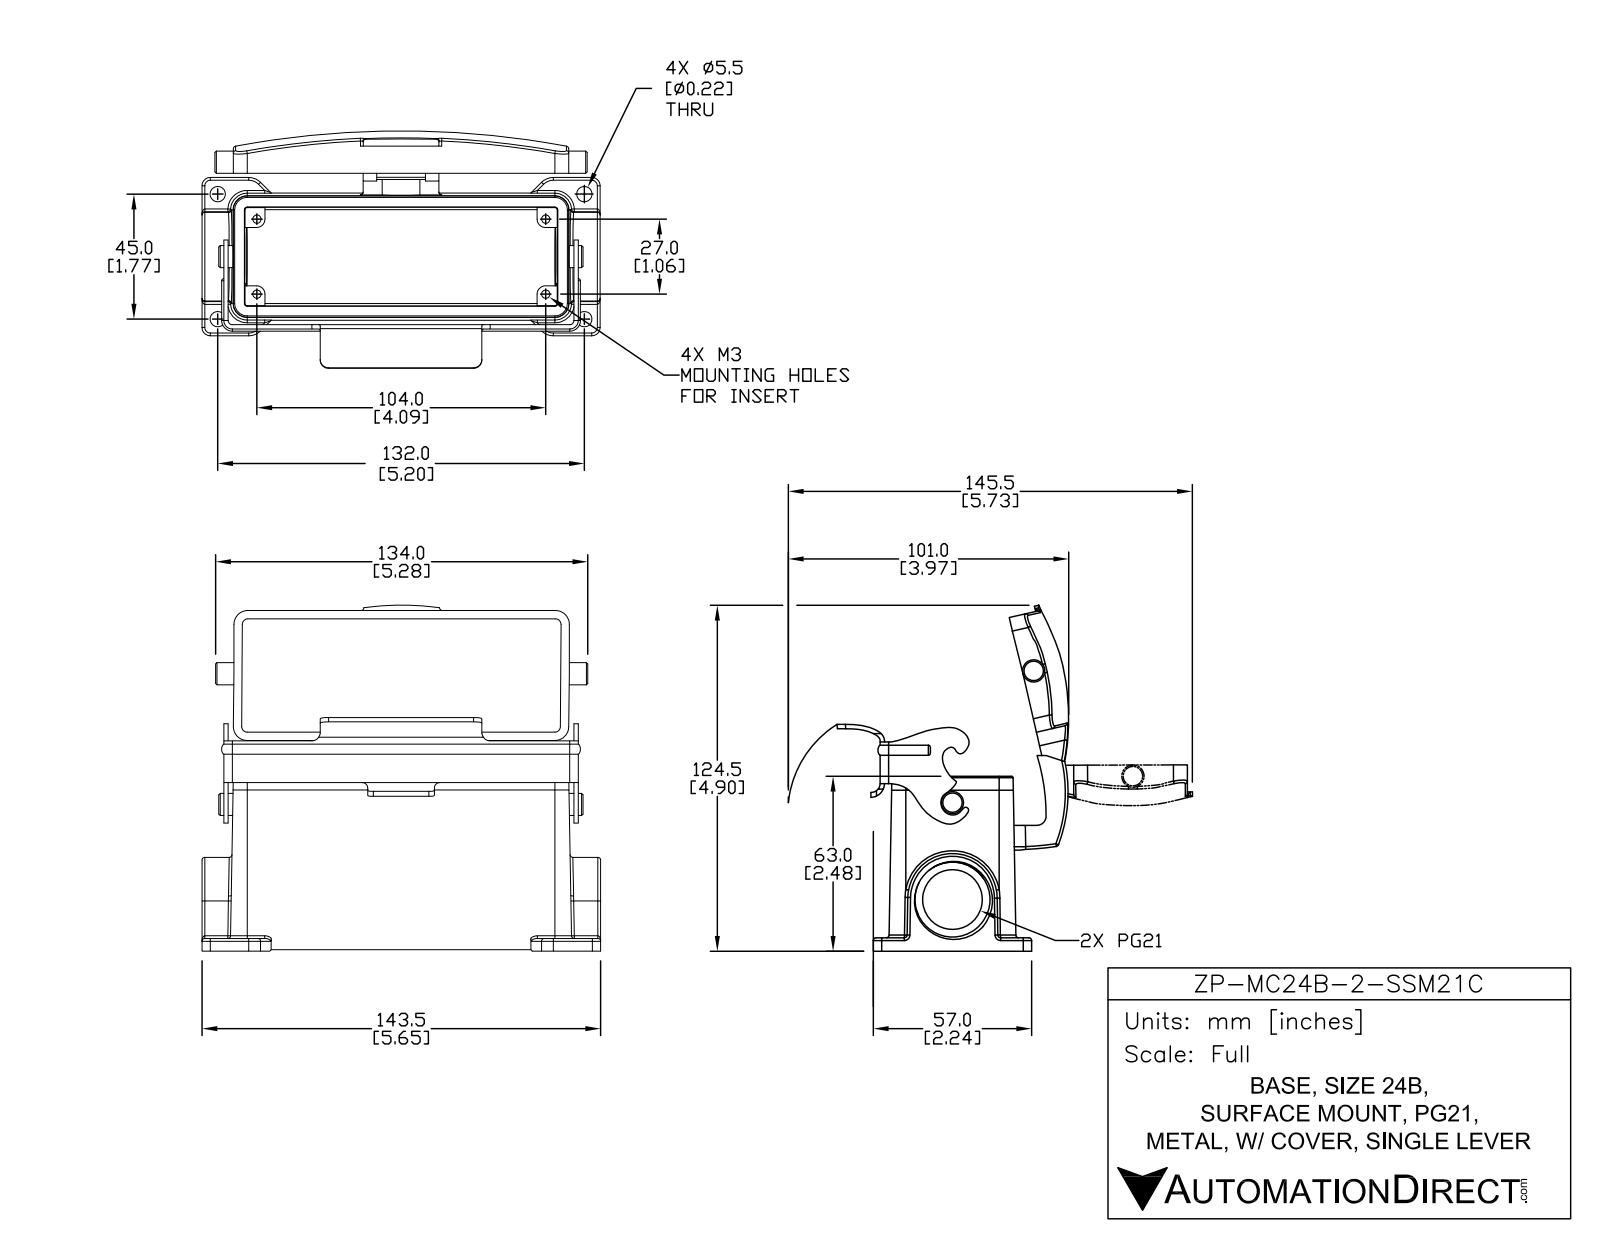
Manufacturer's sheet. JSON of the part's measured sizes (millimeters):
{"part_name": "ZP-MC24B-2-SSM21C", "step_written_by": "SolidWorks 2014 (AUTOMOTIVE_DESIGN)", "units": "millimeters", "bodies": {"solids": 3, "faces": 430, "planar": 151, "cylindrical": 162, "other": 117}, "overall_size": [143.32, 120.93, 85.42], "volume_mm3": 172644, "surface_area_mm2": 86113, "round_holes": [[3, 4], [5.5, 4], [2, 1], [21.5, 1], [27, 1]], "round_bosses_or_shafts": [[8, 1], [7.95, 1], [6.8, 1]], "partial_cylinders_radius": [[1, 22], [3, 12], [2, 8], [5, 6], [0.5, 4], [6, 4], [1.5, 2], [3.06, 2]], "face_to_face_distances": [39.67, 6.22, 0.5, 6.72, 40.5, 3, 1.56, 116.8, 54.5, 119], "hole_center_spacings": [16.64, 38.63, 118.34, 123.37, 27, 45, 104, 107.45]}
